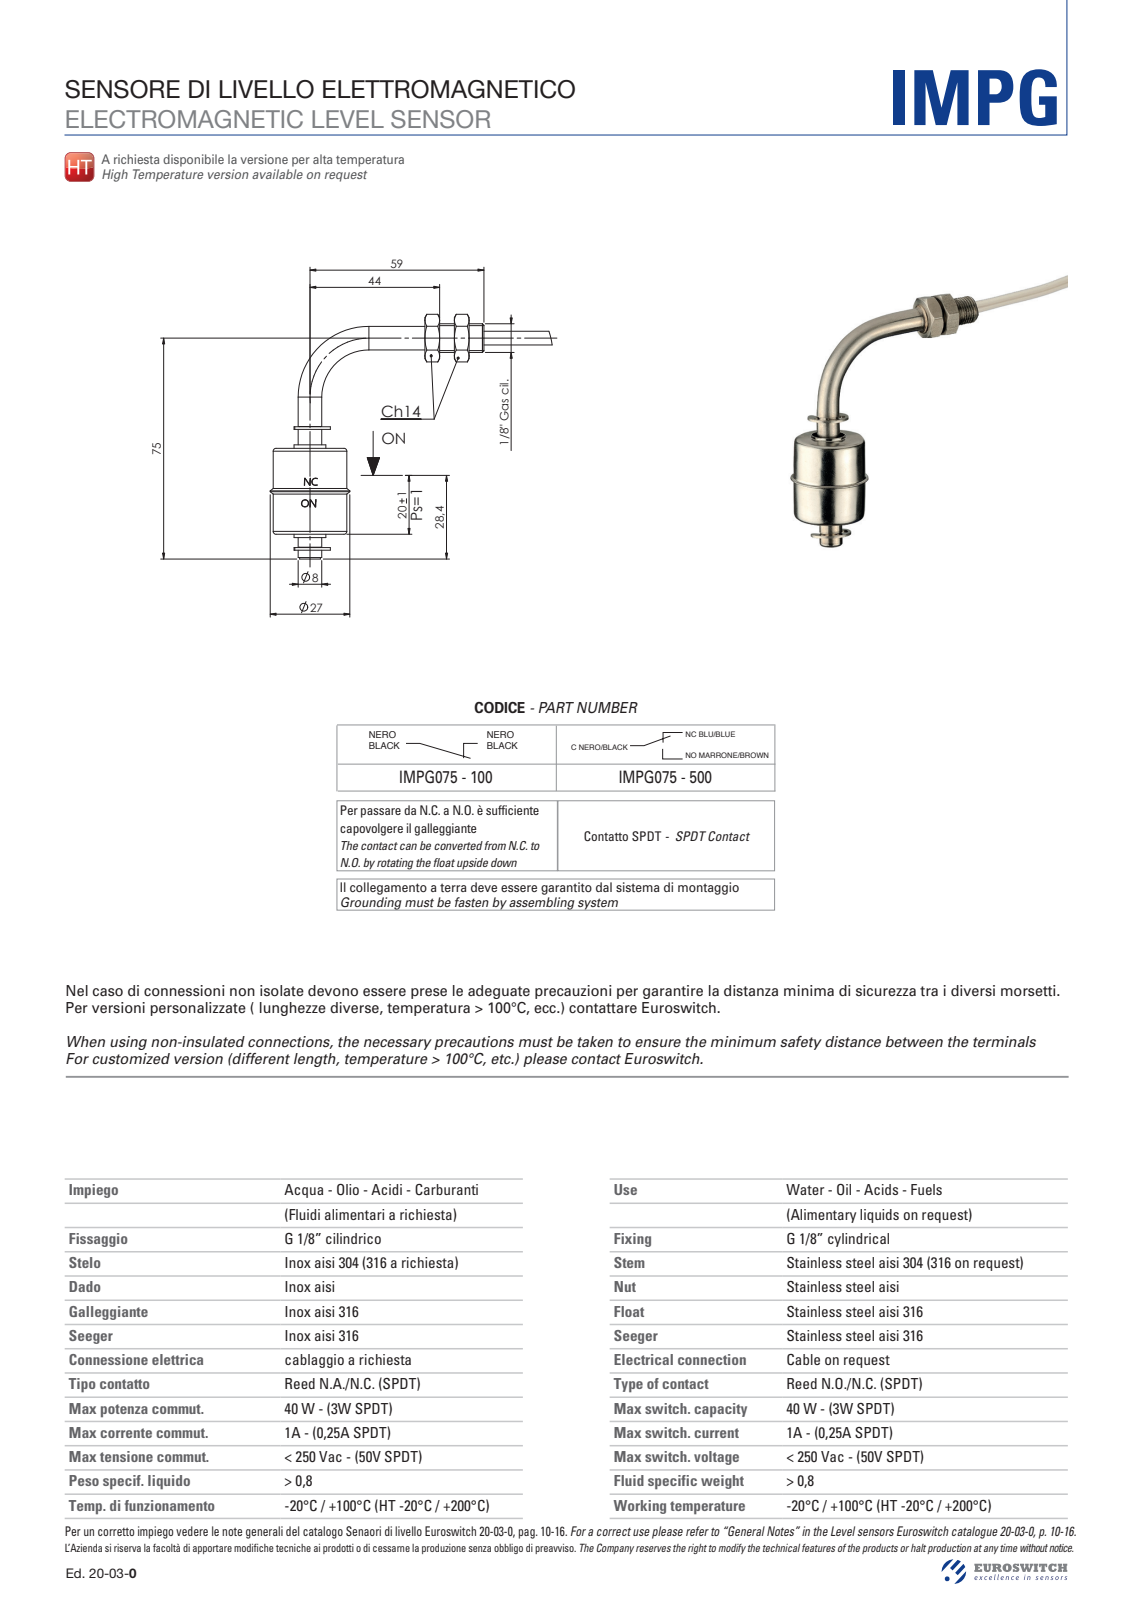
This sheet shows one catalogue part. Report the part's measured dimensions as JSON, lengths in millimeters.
{"part_name": "IMPG", "step_written_by": "SolidWorks 2019 (AUTOMOTIVE_DESIGN)", "units": "millimeters", "bodies": {"solids": 0, "faces": 186, "planar": 68, "cylindrical": 68, "other": 50}, "overall_size": [127.5, 84.81, 27], "round_holes": [[6.5, 1], [9.5, 1], [10.4, 1]], "round_bosses_or_shafts": [[8, 2], [1.6, 2], [0.5, 2], [27, 1], [25, 1], [16.6, 1], [10.8, 1], [9.9, 1]], "partial_cylinders_radius": [[0.5, 3], [1, 2], [5.3, 1], [6.9, 1]], "face_to_face_distances": [2, 29.2, 4, 9, 5, 11, 7, 1.5, 15.5, 41.1]}
